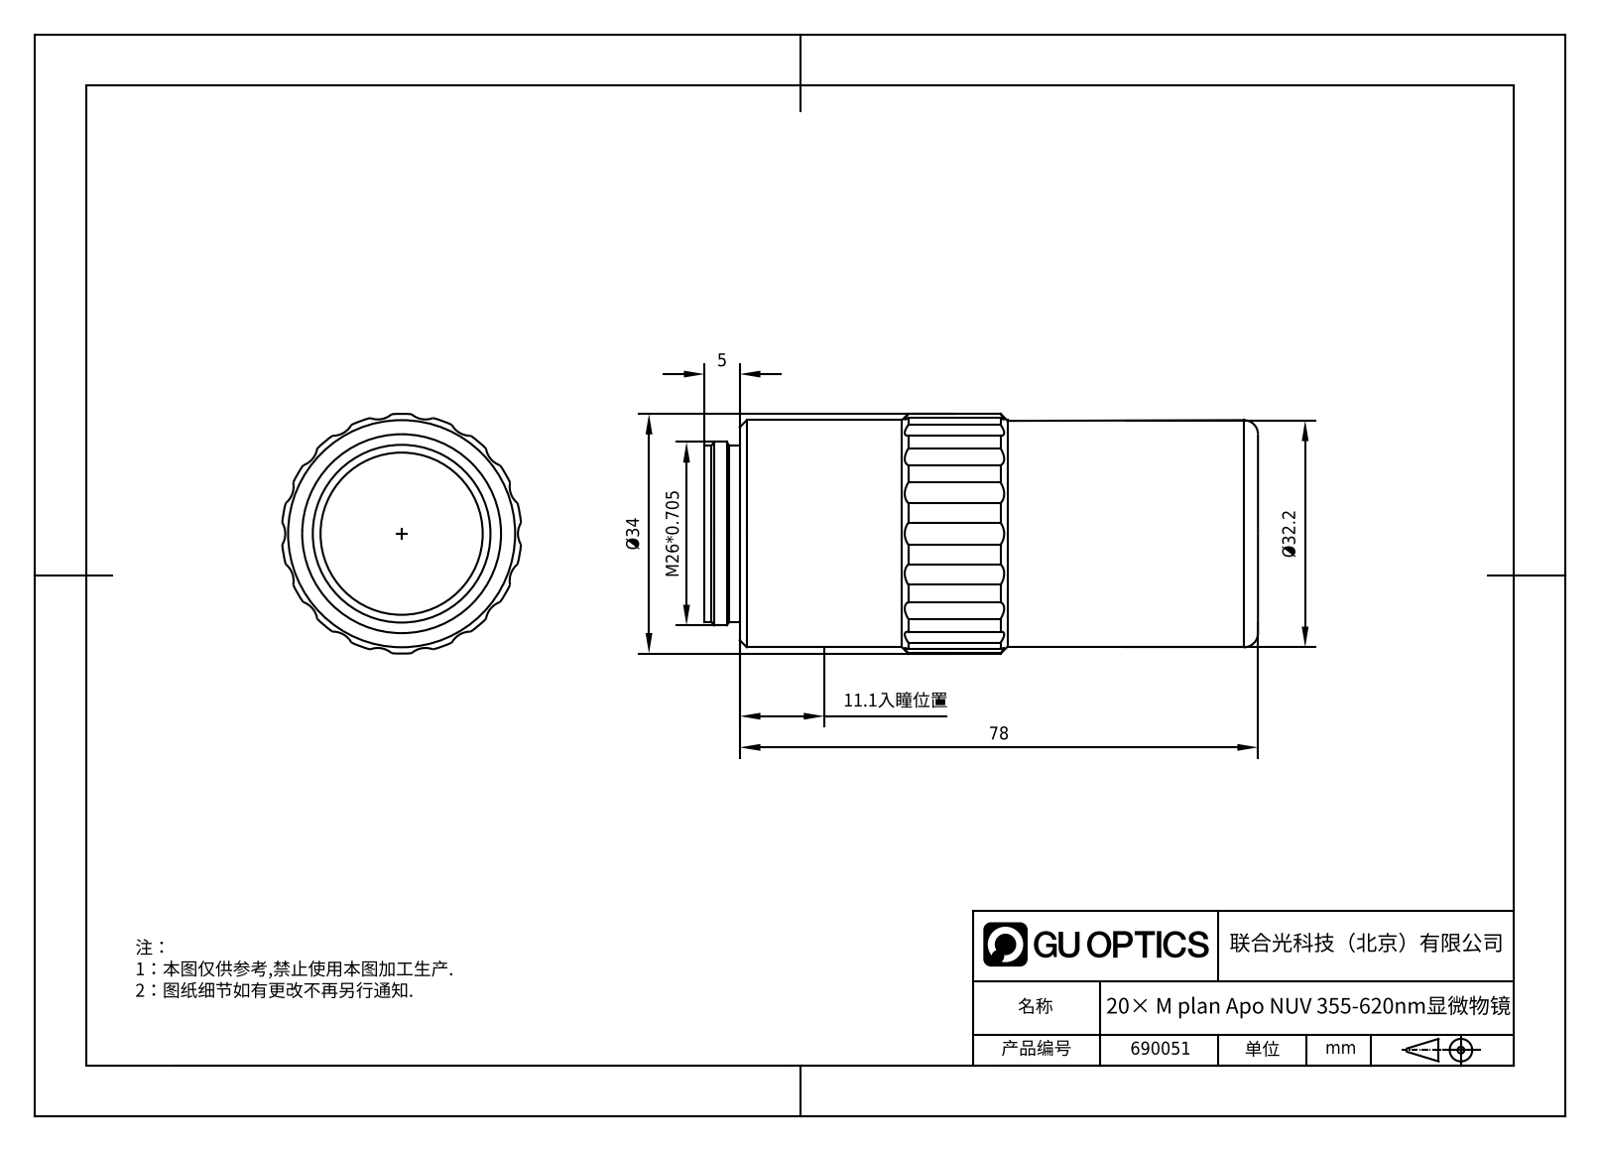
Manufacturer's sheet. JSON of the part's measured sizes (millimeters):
{"part_name": "690051", "step_written_by": "SolidWorks 2020 (AUTOMOTIVE_DESIGN)", "units": "millimeters", "bodies": {"solids": 1, "faces": 55, "planar": 6, "cylindrical": 43, "other": 6}, "overall_size": [83, 34, 33.86], "volume_mm3": 66601, "surface_area_mm2": 10096, "round_holes": [[10, 1], [19.5, 1]], "round_bosses_or_shafts": [[32.2, 1], [26, 1], [25, 1]], "partial_cylinders_radius": [[3, 18], [17, 1]], "face_to_face_distances": [1, 82, 83, 5, 77, 78, 4, 81, 43, 42]}
